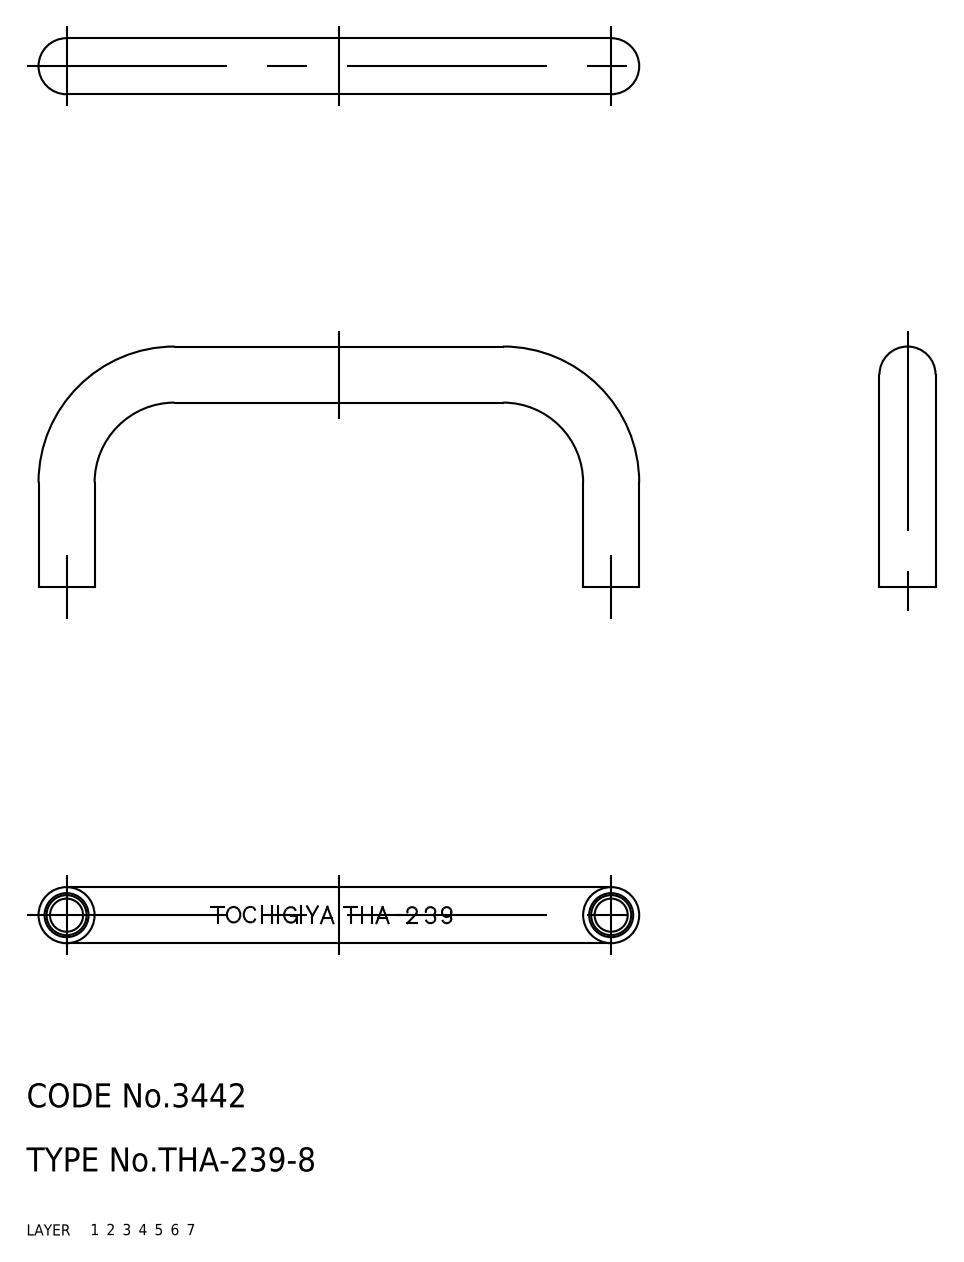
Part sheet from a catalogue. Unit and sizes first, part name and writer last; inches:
Units: inches
Overall size (bounding box): 2.953 × 1.181 × 0.276
Volume: 0.237 in³ · Surface area: 4.241 in²
Bodies: 1 solid, 18 faces (0 planar, 0 cylindrical, 18 other)
Part name (STEP PRODUCT): pull
STEP written by: CADfix (AUTOMOTIVE_DESIGN)
